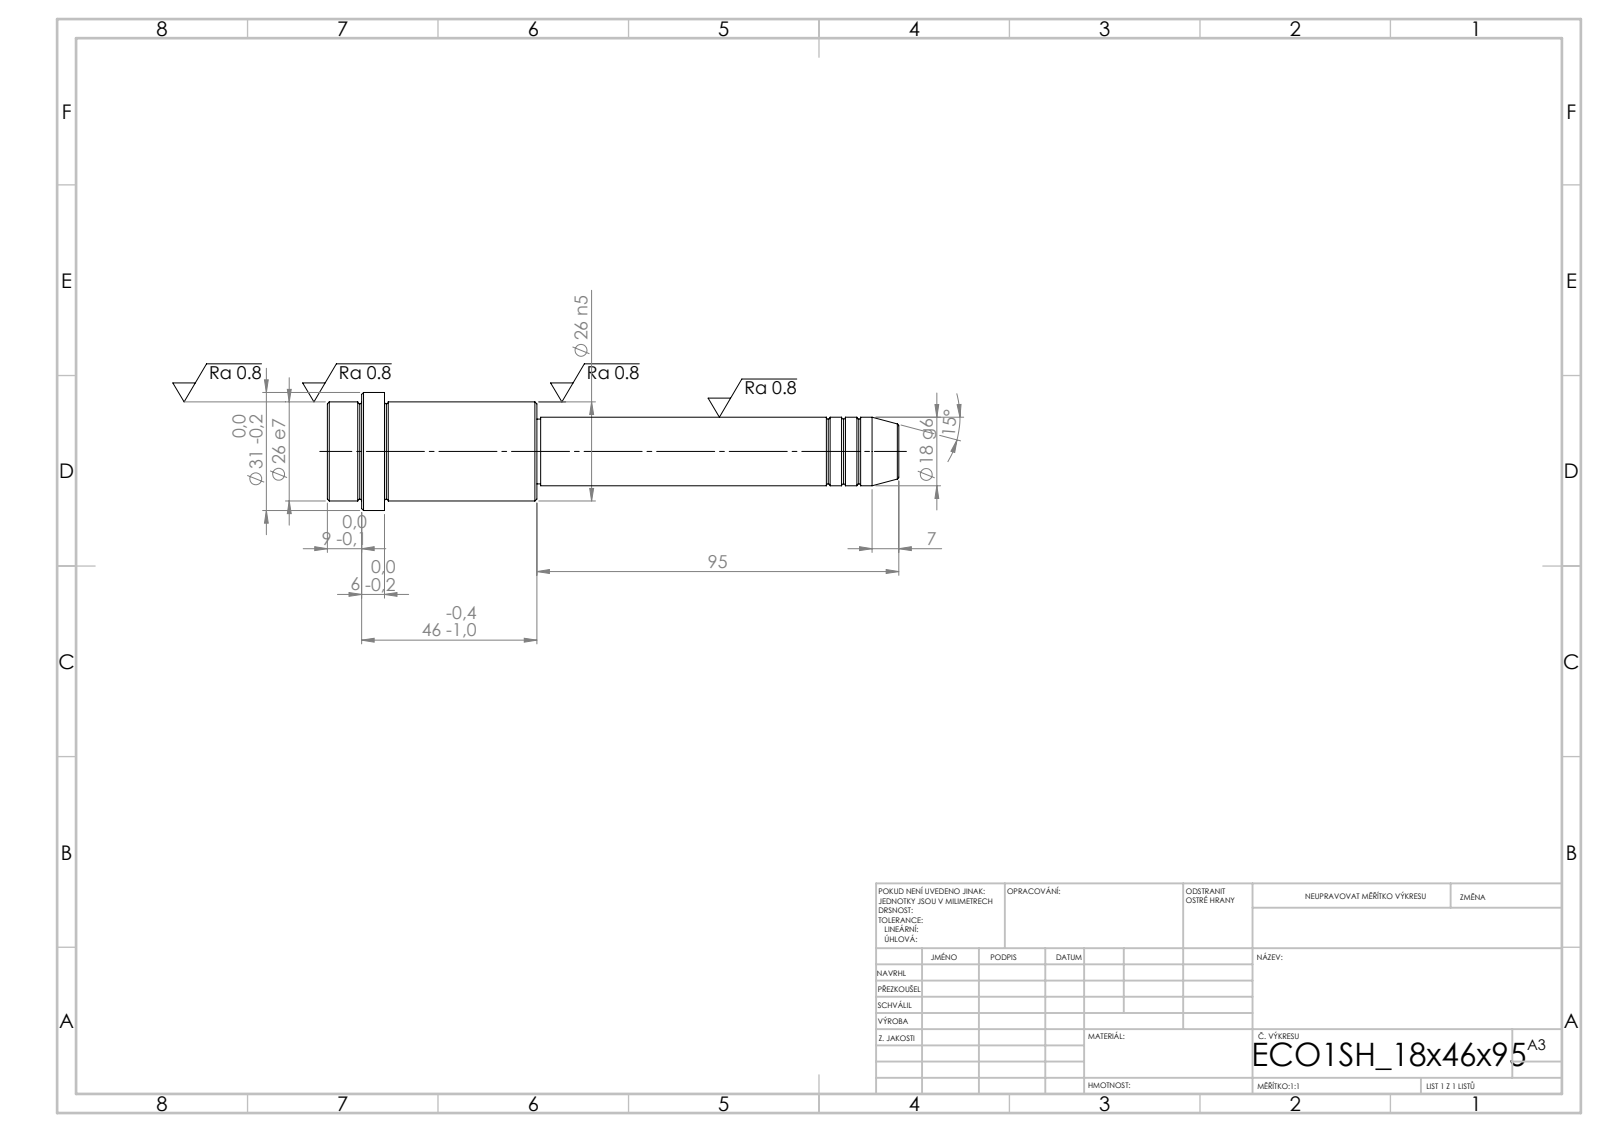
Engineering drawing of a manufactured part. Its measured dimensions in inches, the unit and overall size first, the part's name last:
Units: inches
Overall size (bounding box): 5.906 × 1.22 × 1.22
Round bosses / shafts (diameter × count): ⌀1.22 ×1, ⌀1.024 ×1, ⌀0.709 ×1, ⌀0.669 ×1
Main face-to-face distances: 2.165, 1.575, 0.591, 1.811, 0.236, 0.354, 3.74, 5.315, 5.551, 5.906
Volume: 3.307 in³ · Surface area: 17.81 in²
Bodies: 1 solid, 52 faces (6 planar, 16 cylindrical, 30 other)
STEP written by: SolidWorks 2019 (CONFIG_CONTROL_DESIGN)
